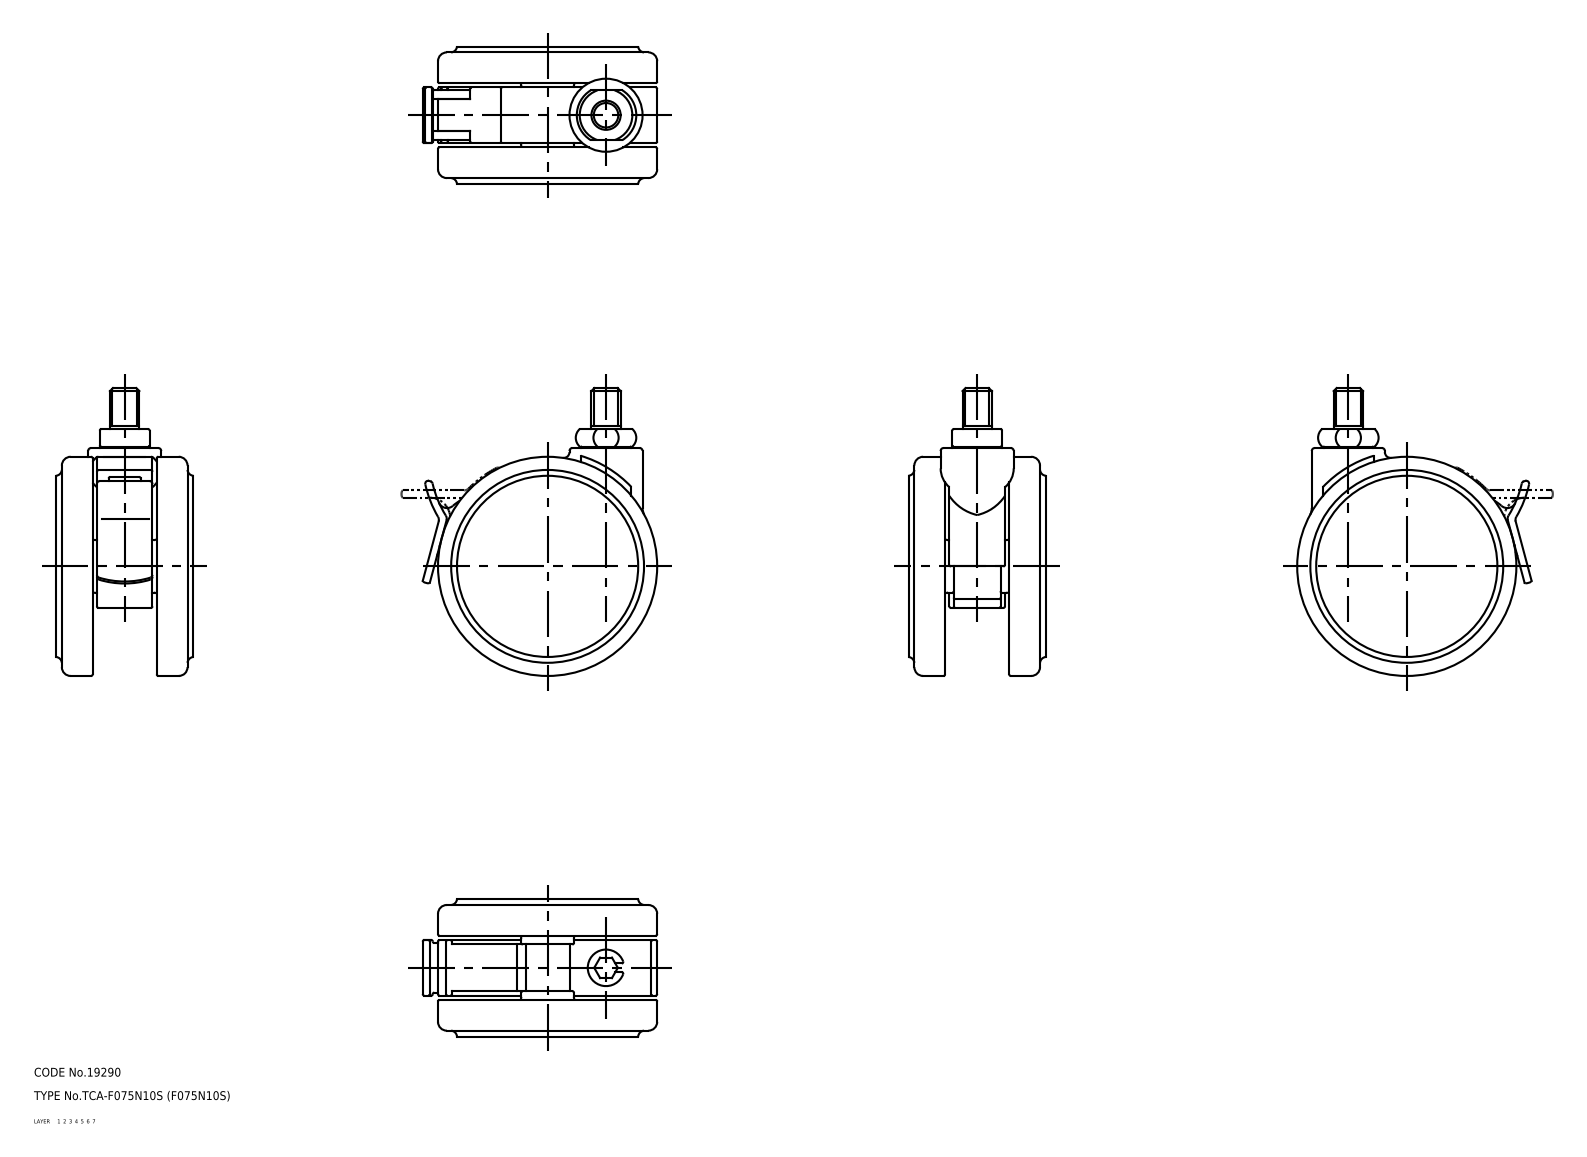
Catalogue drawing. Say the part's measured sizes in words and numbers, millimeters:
The part is named "67124695; 67124708; 67124721; 67124734 (+1 more)". Its 3-D file was written by "CADfix (AUTOMOTIVE_DESIGN)". It is 5 solids with 260 faces: 0 planar, 0 cylindrical and 260 other. Overall it measures 98.5 by 80.25 by 47 millimeters. Its volume is 155 689 cubic millimeters and its surface area 39 530 square millimeters.
